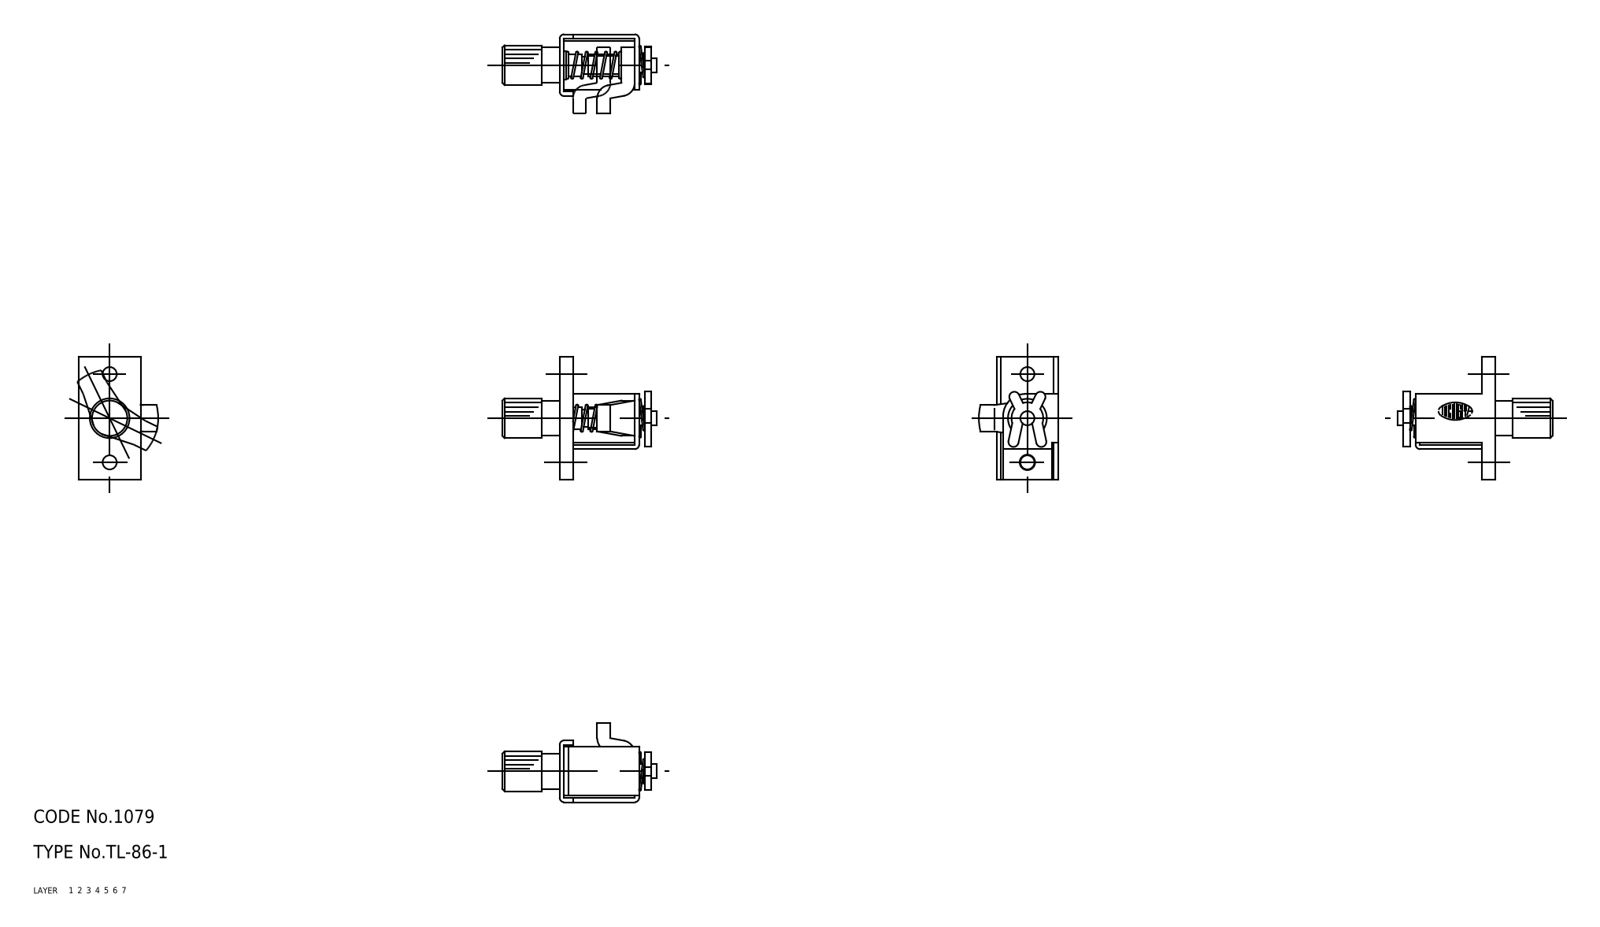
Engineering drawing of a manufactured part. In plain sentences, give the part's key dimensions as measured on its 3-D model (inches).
The part is named "spring_2; spring_1; retainer; knob (+3 more)". Its 3-D file was written by "CADfix (AUTOMOTIVE_DESIGN)". It is 6 solids with 242 faces: 0 planar, 0 cylindrical and 242 other. Overall it measures 1.378 by 1.102 by 0.709 inches. Its volume is 0.154 cubic inches and its surface area 5.715 square inches.
